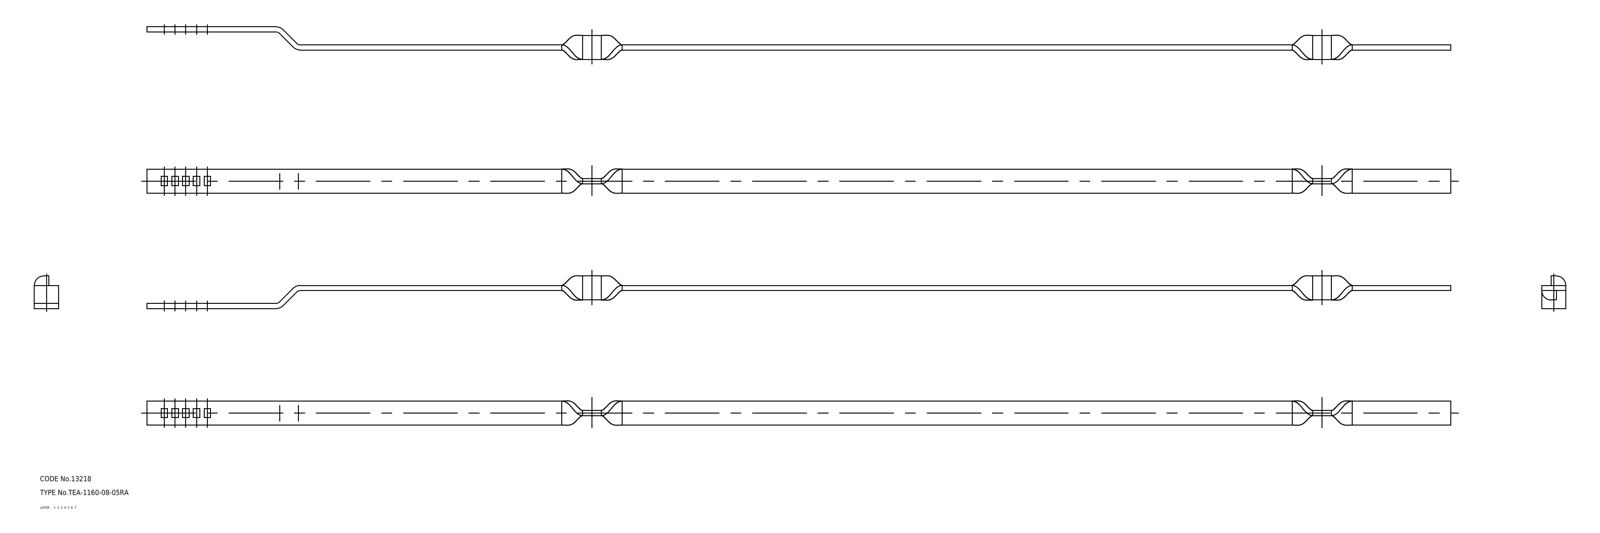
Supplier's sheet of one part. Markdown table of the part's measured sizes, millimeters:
| quantity | value |
| --- | --- |
| part name | rod |
| STEP written by | CADfix (AUTOMOTIVE_DESIGN) |
| units | millimeters |
| bodies | 1 solid, 66 faces (0 planar, 0 cylindrical, 66 other) |
| overall size | 759 × 19.04 × 14.52 |
| volume | 31 720 mm³ |
| surface area | 26 258 mm² |
